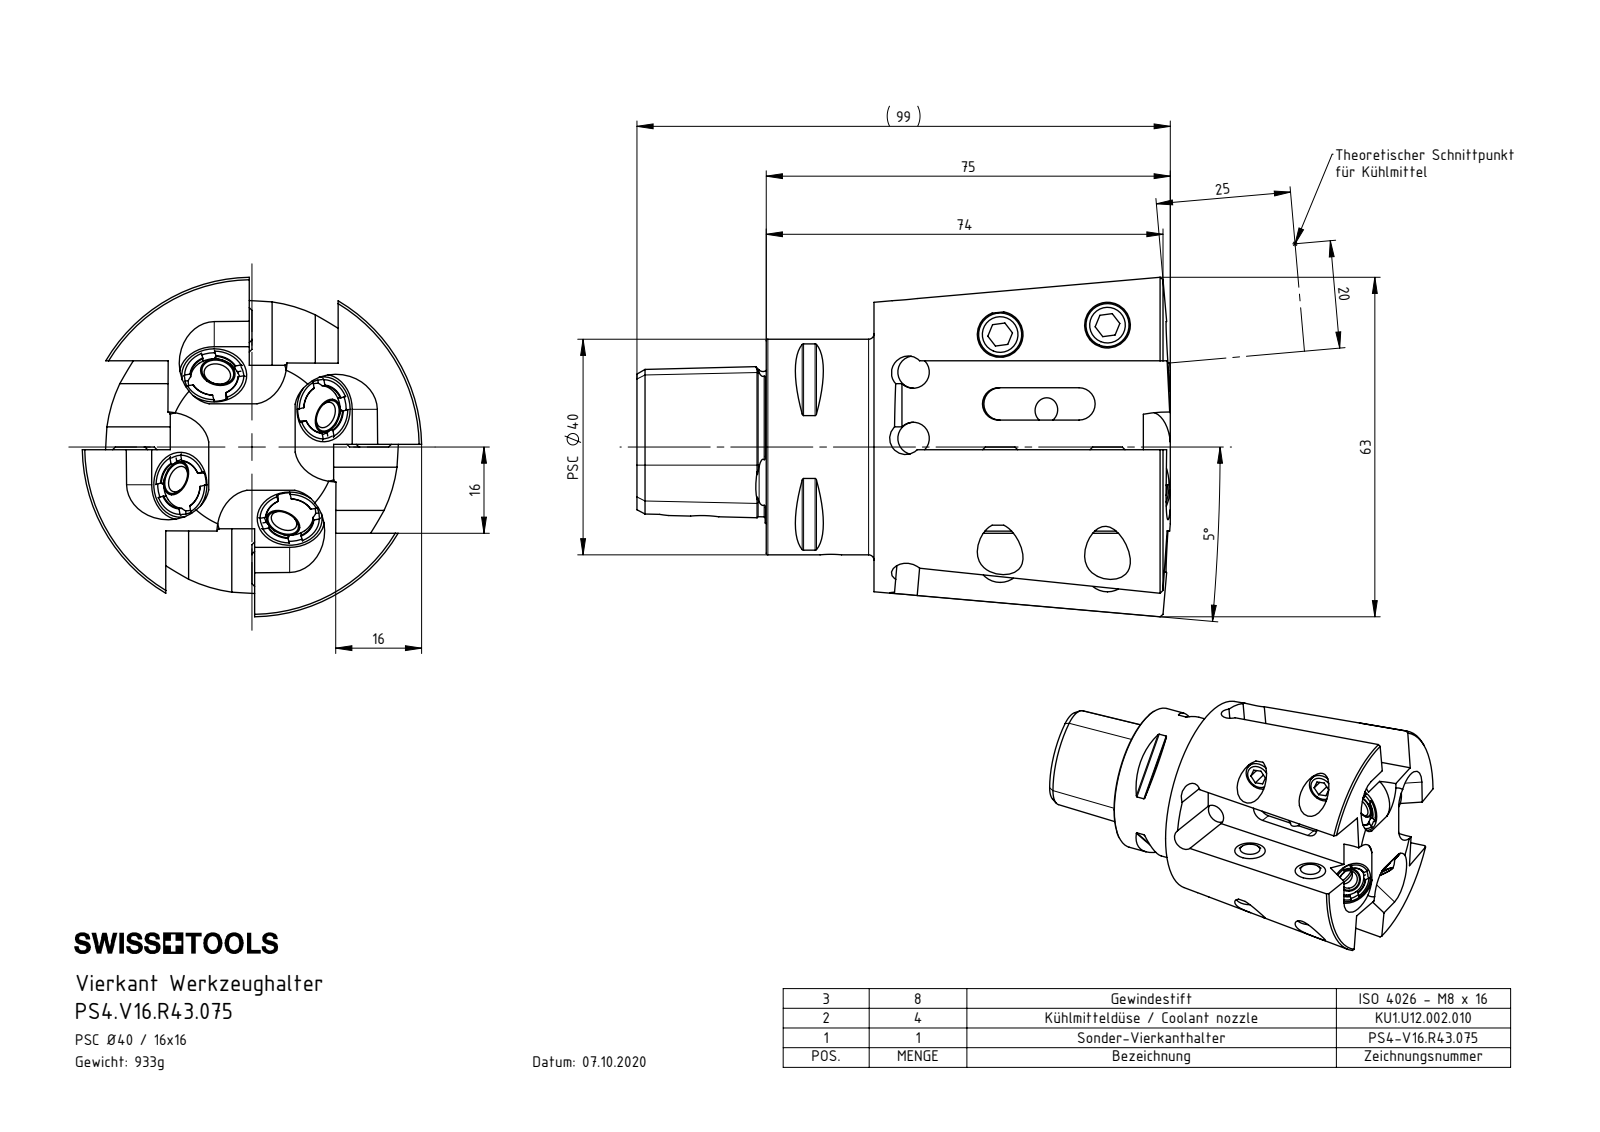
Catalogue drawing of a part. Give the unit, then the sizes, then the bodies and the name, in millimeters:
Units: millimetres
Overall size (bounding box): 99 × 62.98 × 62.98
Round holes (diameter × count): ⌀6.8 ×9, ⌀5 ×8, ⌀6 ×8, ⌀8.5 ×8, ⌀4.2 ×4, ⌀10 ×4, ⌀11 ×4, ⌀4 ×1, ⌀4.6 ×1, ⌀12.5 ×1, ⌀18 ×1, ⌀20 ×1
Round bosses / shafts (diameter × count): ⌀8 ×8, ⌀12 ×4, ⌀40 ×1
Partial cylindrical surfaces — rounded edges, fillets, slot ends (radius × count): R3 ×9, R0.3 ×8, R6.5 ×8, R4.4 ×4
Main face-to-face distances: 15.5, 16.5, 1, 32, 16, 5, 11, 20, 3, 0.5
Hole centre spacings: 12.3, 20, 47.83, 4.01, 37.72, 41.74, 45.22, 56.1
Volume: 115 842 mm³ · Surface area: 41 027 mm²
Bodies: 21 solids, 494 faces (200 planar, 110 cylindrical, 184 other)
Part name (STEP PRODUCT): PS4.V16.R43.075; KU1-U12.002.010; KU1-U12.003.010_B; ISO 4026 - M8 x 16 (+3 more)
STEP written by: SolidWorks 2017 (AUTOMOTIVE_DESIGN)
